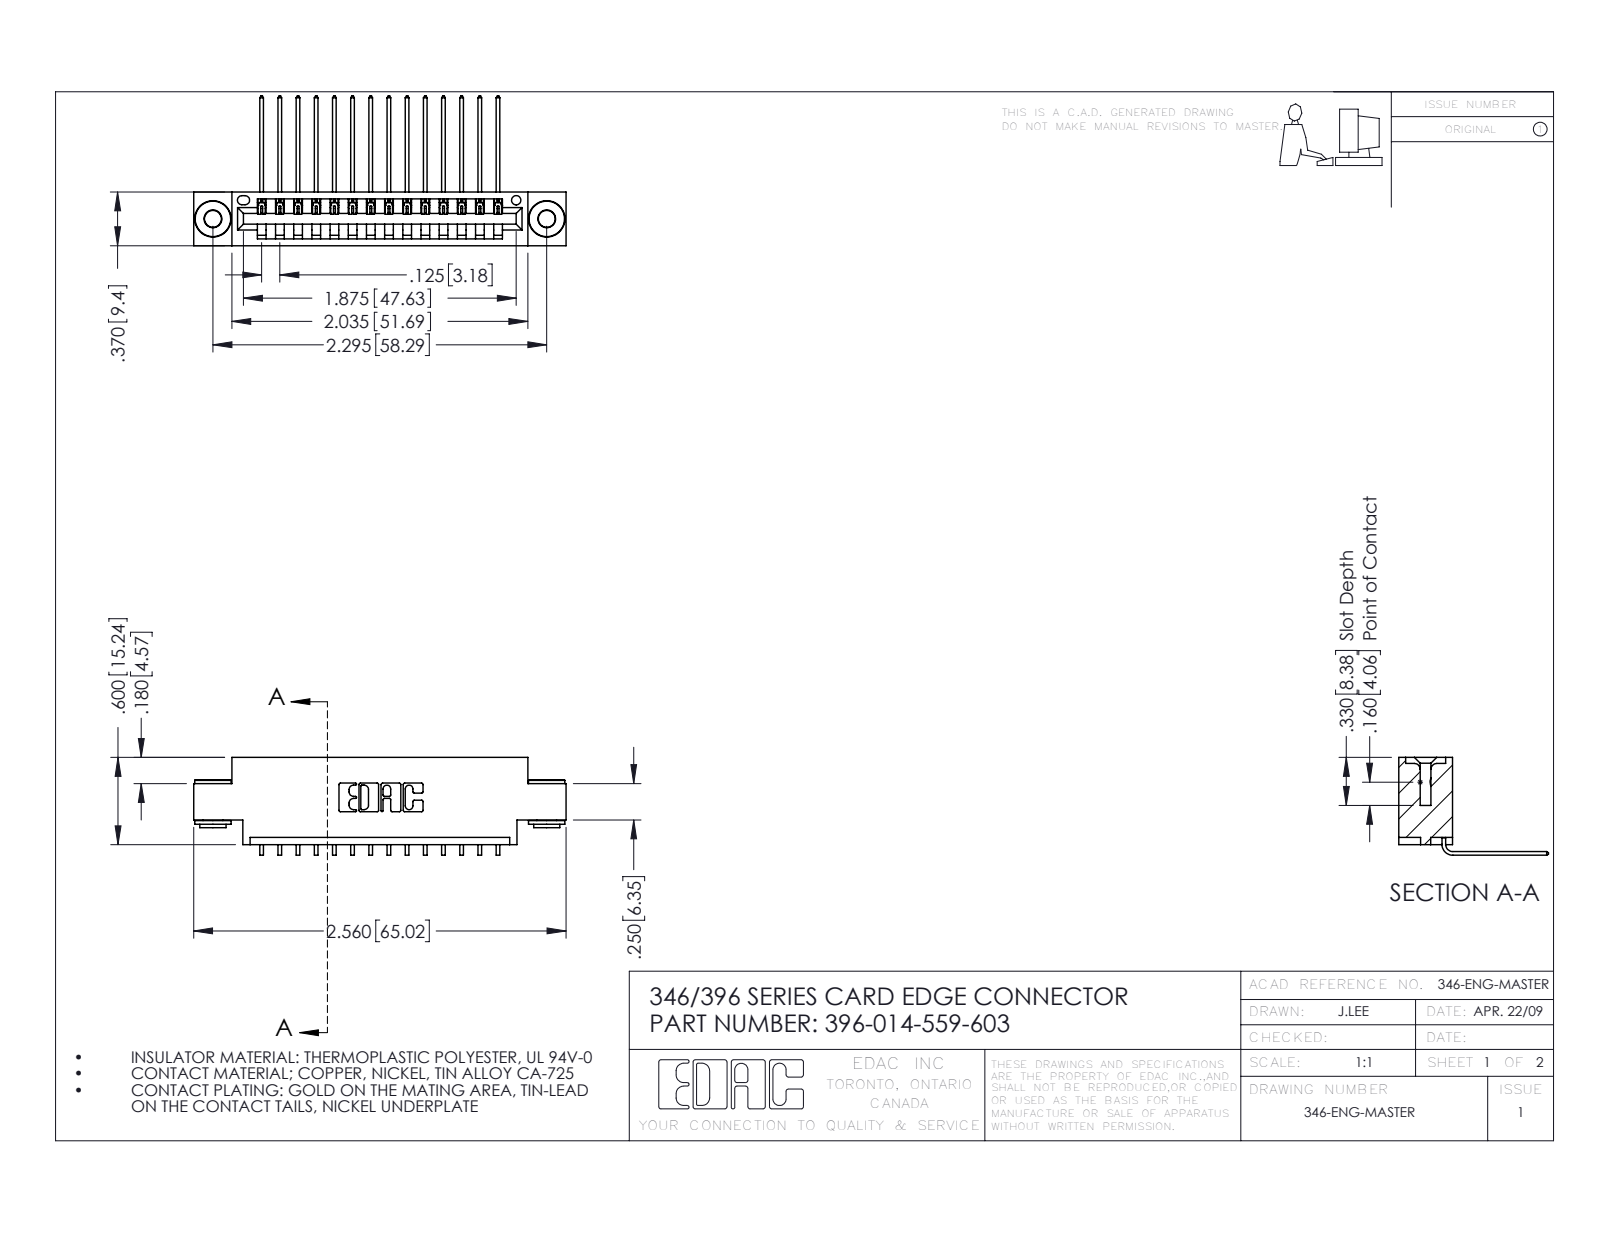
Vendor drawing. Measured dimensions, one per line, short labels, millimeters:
name: 346 Part_0.170 Offset - 0.156 Dia-TH; 396-014-559-603; 345-292-001_558 559 Tail - 1; 345-250-002_345-250-002-102
written by: SolidWorks 2016 (CONFIG_CONTROL_DESIGN)
unit: mm
bodies: 17 solids, 1004 faces (678 planar, 318 cylindrical, 8 other)
size: 65 × 26.2 × 17.1
volume: 5 950 mm³; area: 7 781 mm²
holes: 2× ⌀2.9, 2× ⌀4, 1× ⌀1.6
bosses: 2× ⌀6.4, 2× ⌀4.6, 2× ⌀3.5
rounds: 28× R0.2, 22× R0.3, 6× R0.2, 6× R0.8, 3× R0.7, 2× R0.8, 2× R1, 1× R0.4
face distances: 9.4, 1.2, 8.2, 6.4, 0.6, 1.8, 3.8, 5.6, 2.5, 4.4
hole spacings: 6.2, 53.1, 58.3
